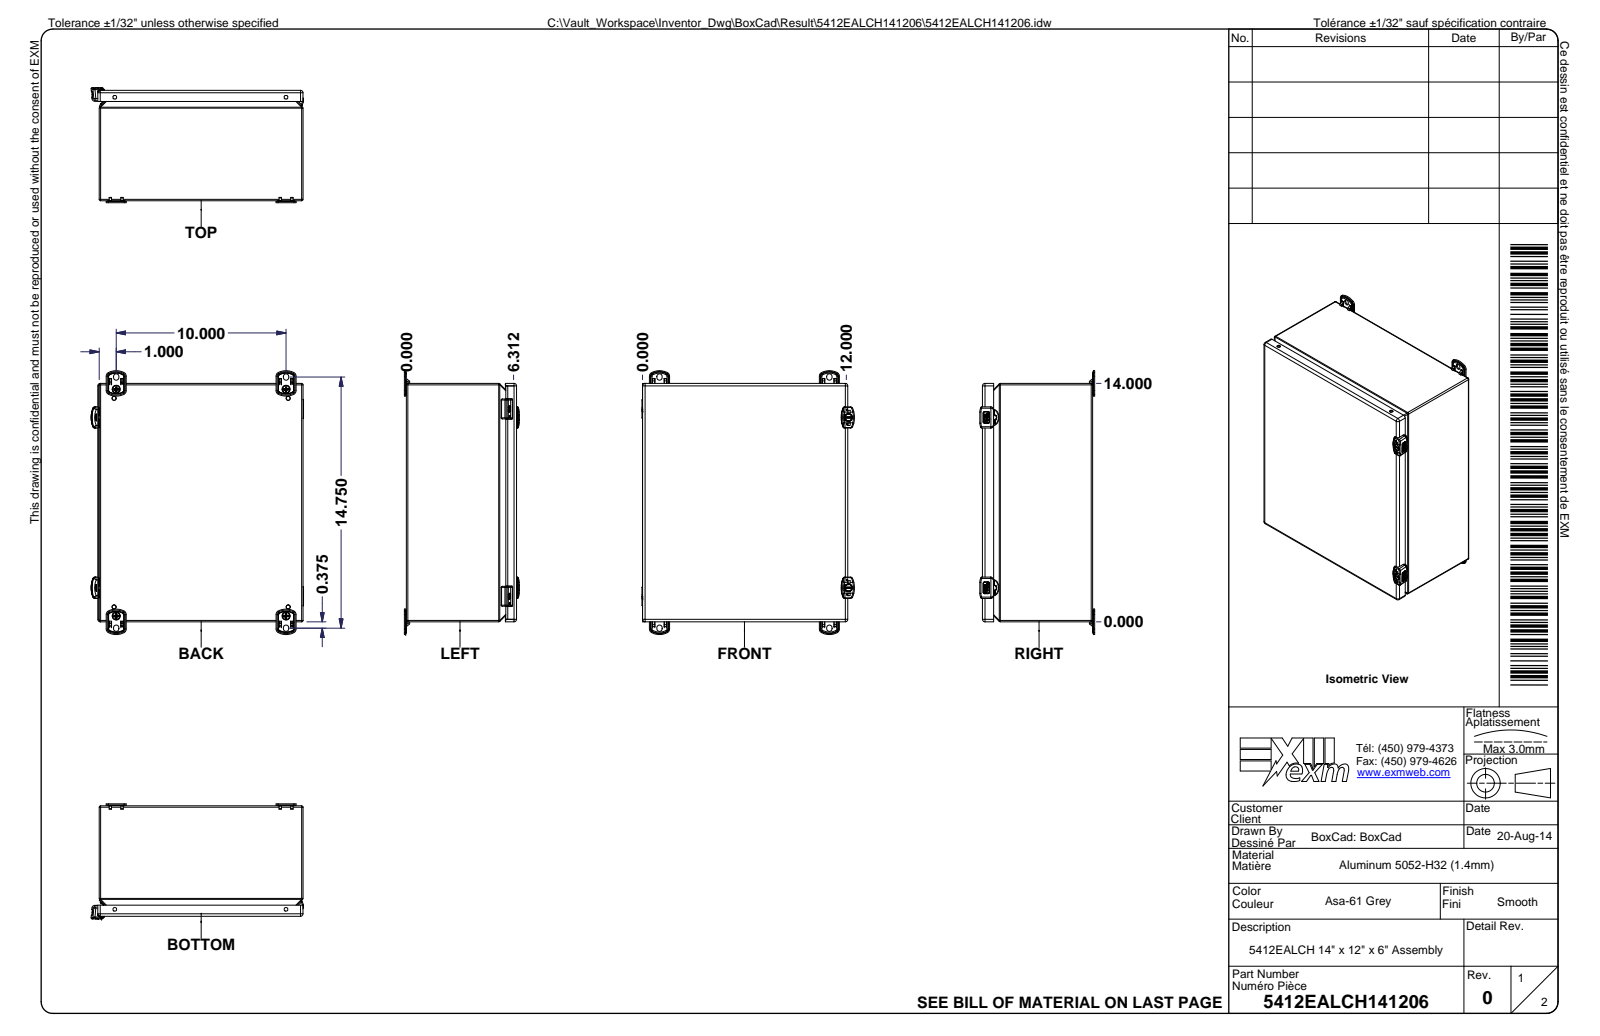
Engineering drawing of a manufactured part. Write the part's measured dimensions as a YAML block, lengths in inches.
part_name: "5412EALCH141206; 5412EALCH141206B; 5412EALCH141206B-P; STK-A-70469-1 (+8 more)"
step_written_by: "Autodesk Inventor 2020 (AUTOMOTIVE_DESIGN)"
units: inches
bodies: {solids: 59, faces: 8409, planar: 3583, cylindrical: 2002, other: 2824}
overall_size: [15.496, 12.503, 6.76]
volume: 51.53
surface_area: 1832
round_holes:
  - {diameter: 0.165, count: 4}
  - {diameter: 0.173, count: 4}
  - {diameter: 0.197, count: 4}
  - {diameter: 0.197, count: 4}
  - {diameter: 0.236, count: 4}
  - {diameter: 0.236, count: 4}
  - {diameter: 0.32, count: 4}
  - {diameter: 0.03, count: 2}
  - {diameter: 0.175, count: 2}
  - {diameter: 0.201, count: 2}
  - {diameter: 0.24, count: 2}
  - {diameter: 0.339, count: 2}
round_bosses_or_shafts:
  - {diameter: 0.232, count: 8}
  - {diameter: 0.5, count: 4}
  - {diameter: 0.3, count: 4}
  - {diameter: 0.236, count: 4}
  - {diameter: 0.193, count: 4}
  - {diameter: 0.197, count: 3}
  - {diameter: 0.412, count: 2}
  - {diameter: 0.394, count: 2}
partial_cylinders:
  - {radius: 0.02, count: 257}
  - {radius: 0.01, count: 209}
  - {radius: 0.039, count: 92}
  - {radius: 0.004, count: 64}
  - {radius: 0.008, count: 60}
  - {radius: 0.059, count: 57}
  - {radius: 0.031, count: 35}
  - {radius: 0.005, count: 33}
face_to_face_distances: [0.053, 0.053, 6.433, 6.38, 6.486, 6.433, 11.947, 0.236, 0.304, 0.357]
hole_center_spacings: [0.546, 12.781, 12.25, 10, 10.139, 11.17, 16.305, 1.506]
